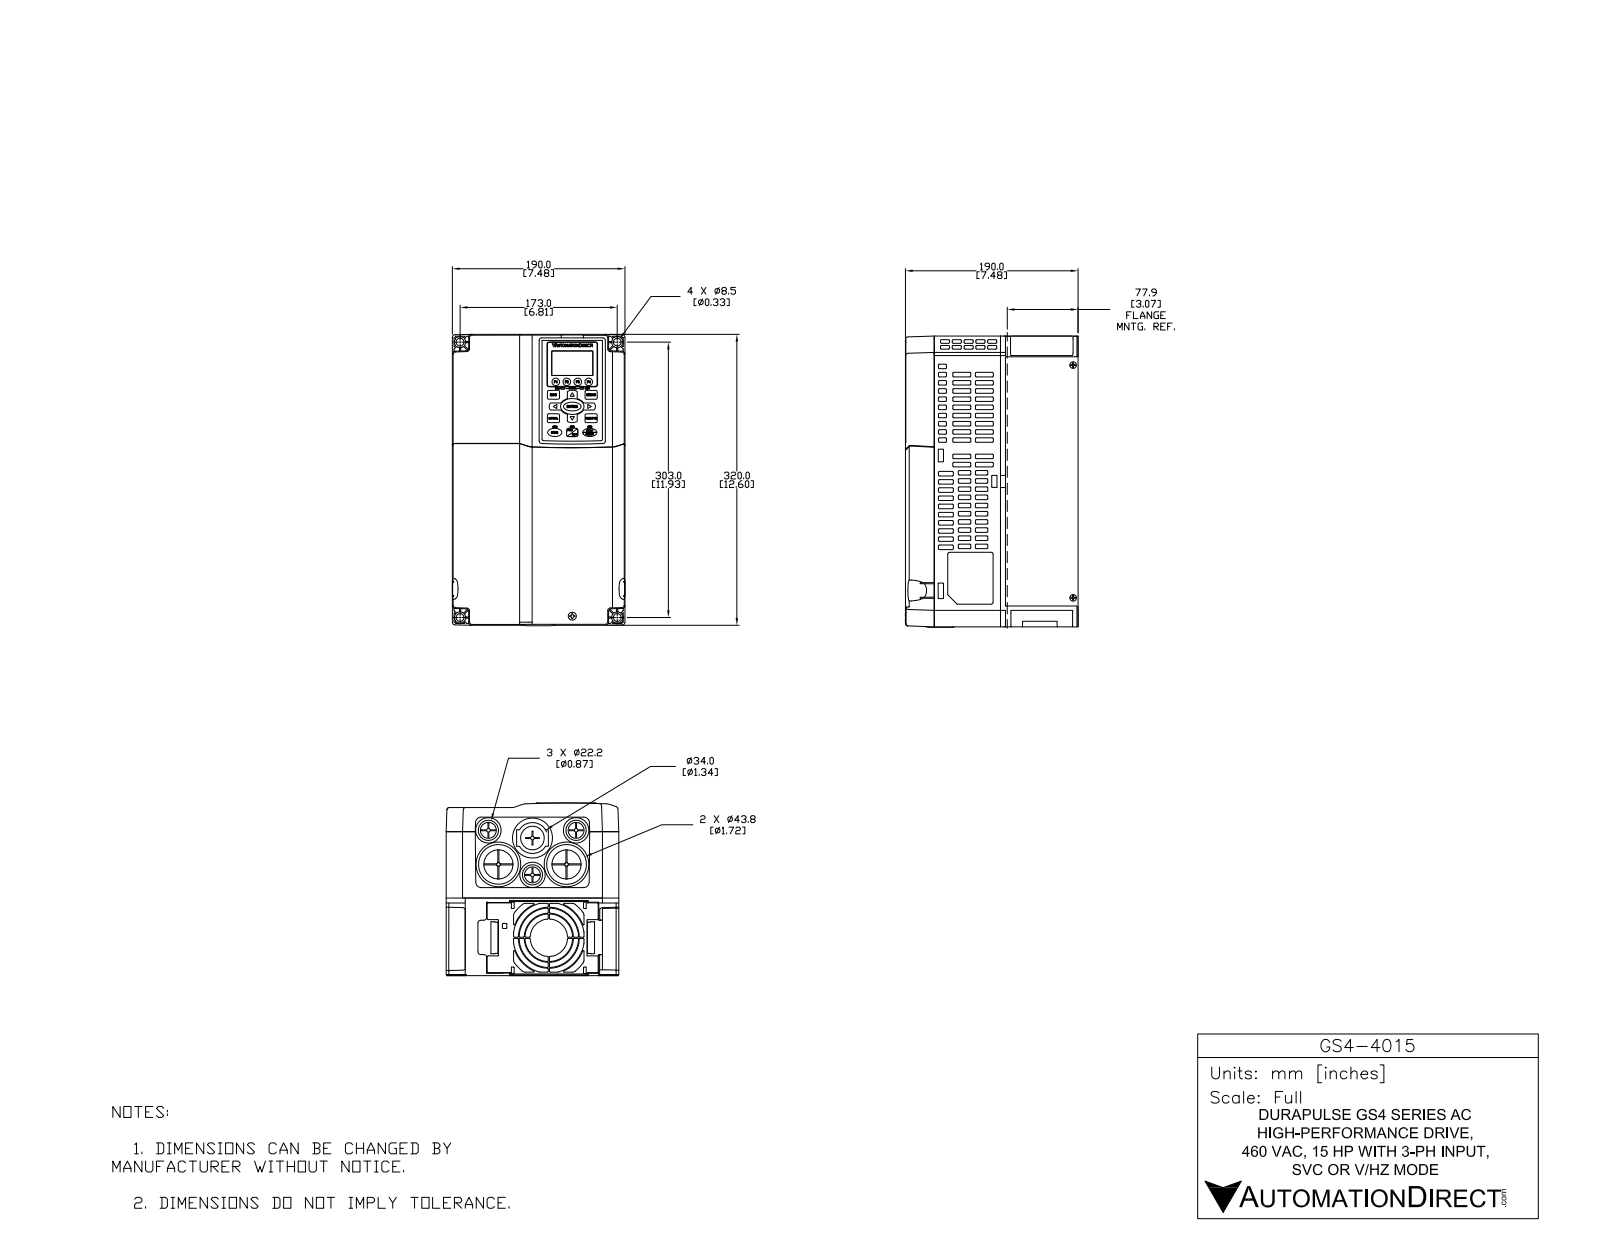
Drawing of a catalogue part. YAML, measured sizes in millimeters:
part_name: "GS4-2010 EXT 1 red 1b extb Thickn 2 COMPLETE NEW ext1 cut2 -surf Db"
step_written_by: "SolidWorks 2017 (AUTOMOTIVE_DESIGN)"
units: millimeters
bodies: {solids: 4, faces: 2399, planar: 1330, cylindrical: 138, other: 931}
overall_size: [320.68, 191.21, 190]
volume: 7277000
surface_area: 863396
round_holes:
  - {diameter: 8.64, count: 4}
partial_cylinders:
  - {radius: 1.31, count: 51}
  - {radius: 2.54, count: 16}
  - {radius: 2, count: 6}
  - {radius: 4.3, count: 6}
  - {radius: 1.49, count: 4}
  - {radius: 3, count: 4}
  - {radius: 3.14, count: 4}
  - {radius: 5.05, count: 4}
face_to_face_distances: [1.91, 18, 172, 4.19, 81.55, 77.36, 25.42, 164.58, 7.42, 146.58]
hole_center_spacings: [173, 303, 348.91]
